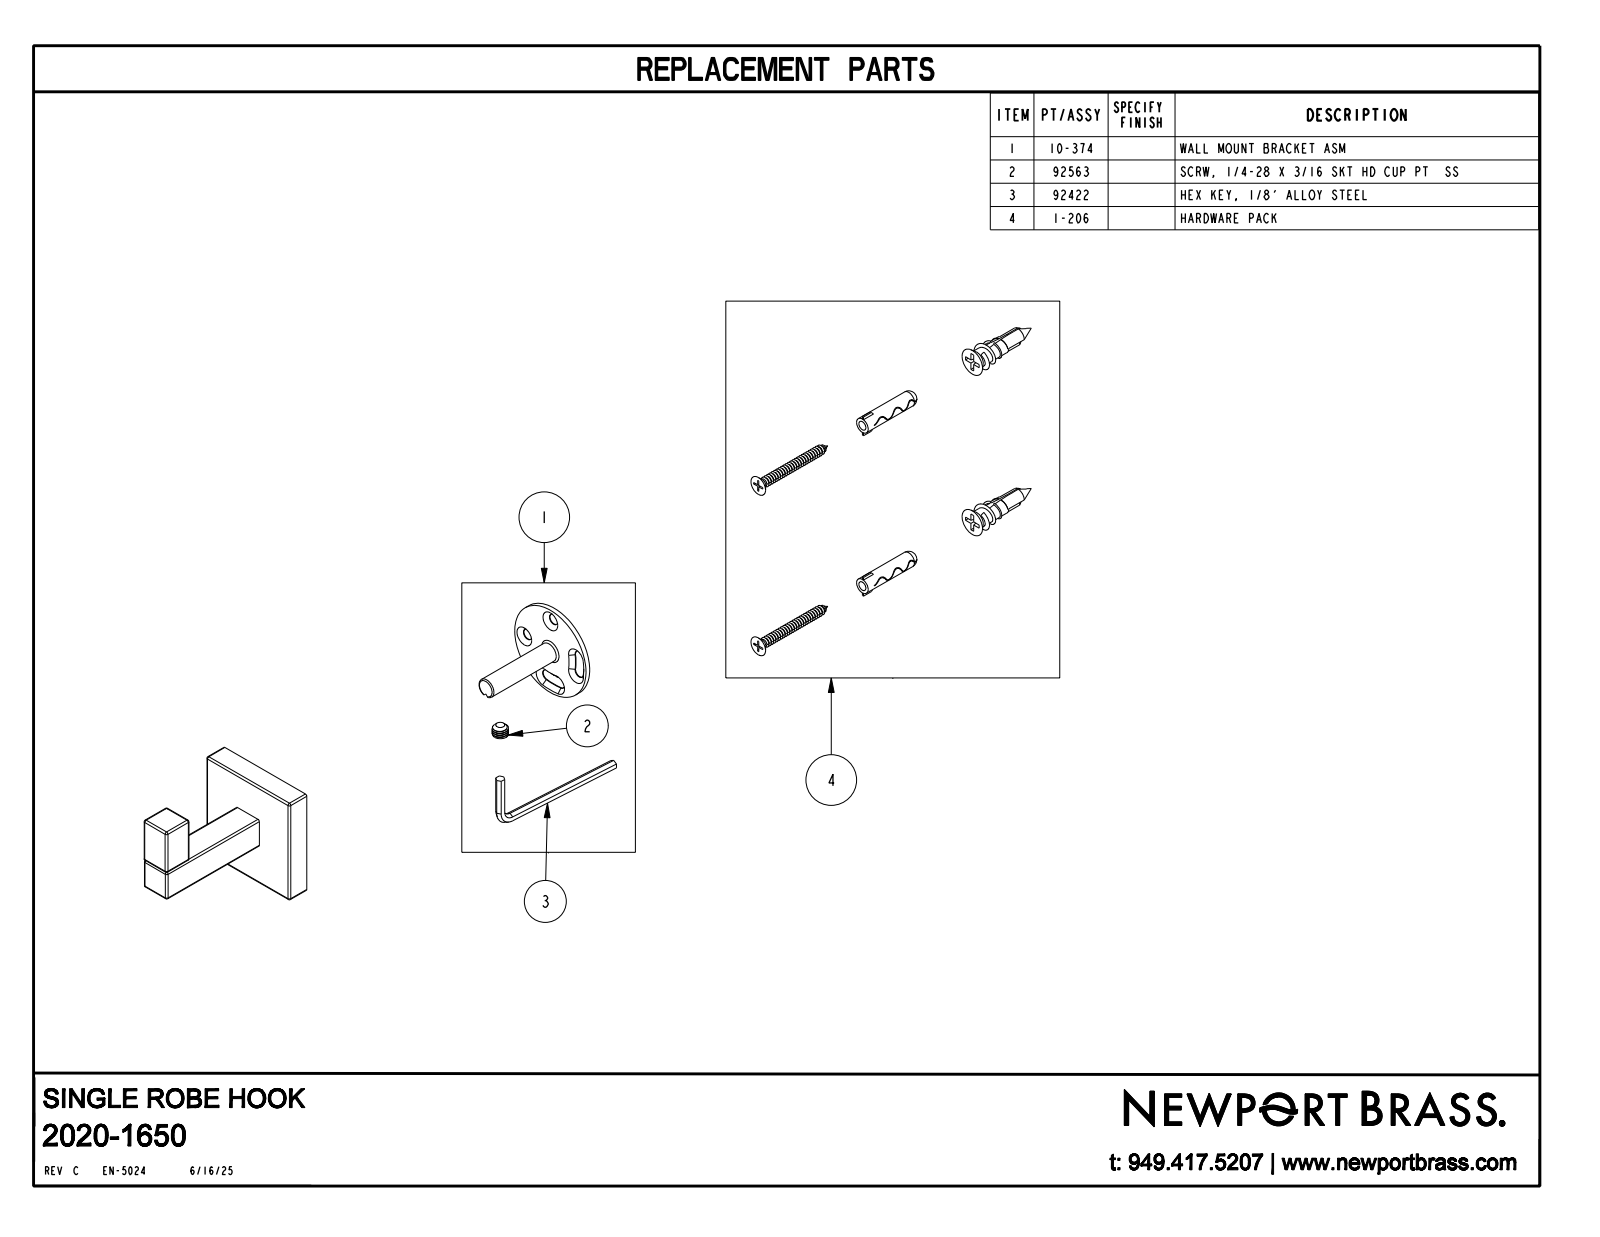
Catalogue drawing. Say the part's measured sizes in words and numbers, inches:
The part is named "2020-1650". Its 3-D file was written by "CREO PARAMETRIC BY PTC INC, 2018400 (CONFIG_CONTROL_DESIGN)". It is 1 solid with 61 faces: 17 planar, 28 cylindrical and 16 other. Overall it measures 2.38 by 1.94 by 1.8 inches. Its volume is 1.898 cubic inches and its surface area 14.46 square inches. Partial cylindrical surfaces (rounded edges, fillets, slot ends): 28 of radius 0.03. The main face-to-face distances are 0.375, 0.5, 1.8, 0.65, 1.15, 0.69, 1.19, 1.11, 0.61, 1.88.
